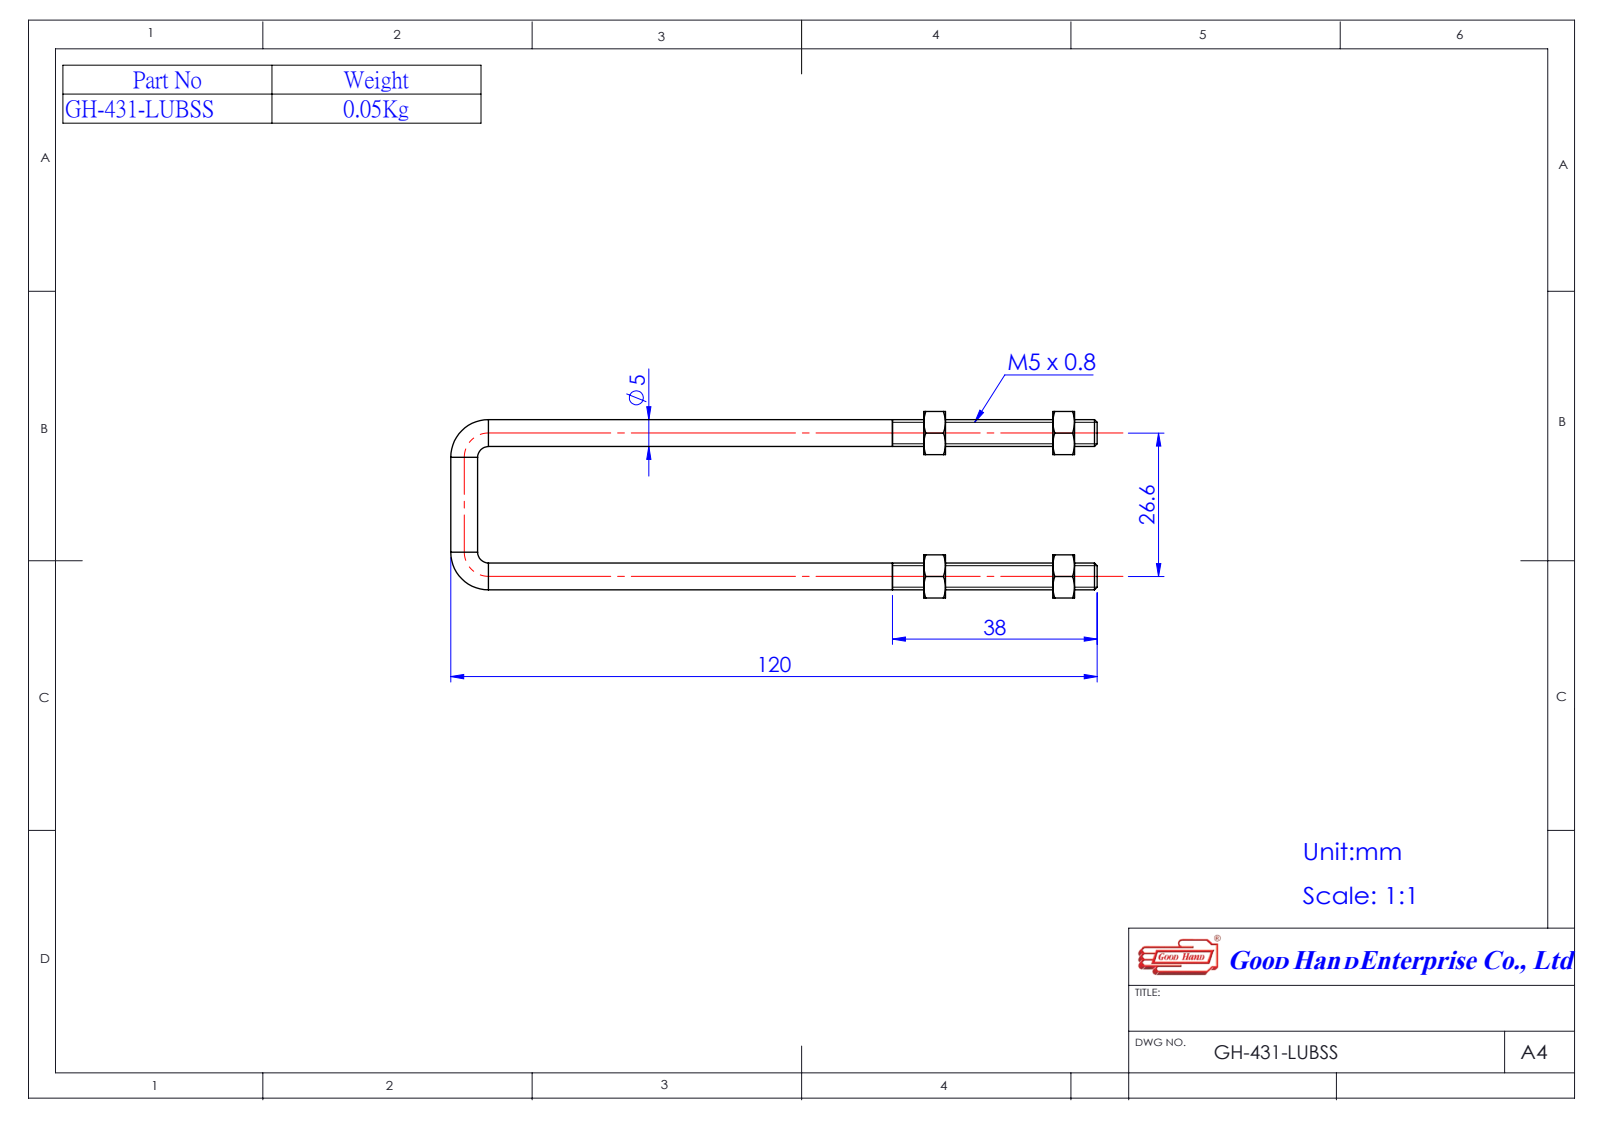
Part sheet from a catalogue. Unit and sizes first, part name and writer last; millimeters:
Units: millimetres
Overall size (bounding box): 120 × 34.6 × 9.24
Round holes (diameter × count): ⌀4.2 ×2, ⌀5 ×2
Round bosses / shafts (diameter × count): ⌀5 ×1
Main face-to-face distances: 8, 13.3, 23.96, 4, 26.6, 21.3, 5.3, 9.83, 33.79, 5.83
Hole centre spacings: 26.6
Volume: 5 711 mm³ · Surface area: 5 104 mm²
Bodies: 7 solids, 136 faces (38 planar, 26 cylindrical, 72 other)
Part name (STEP PRODUCT): 443144; GH-431-LUBSS; Hexagon Nut_2_JIS_JIS B 1181 Hexagon nut - Class 2 Finished M5 --N
STEP written by: SolidWorks 2016 (AUTOMOTIVE_DESIGN)
